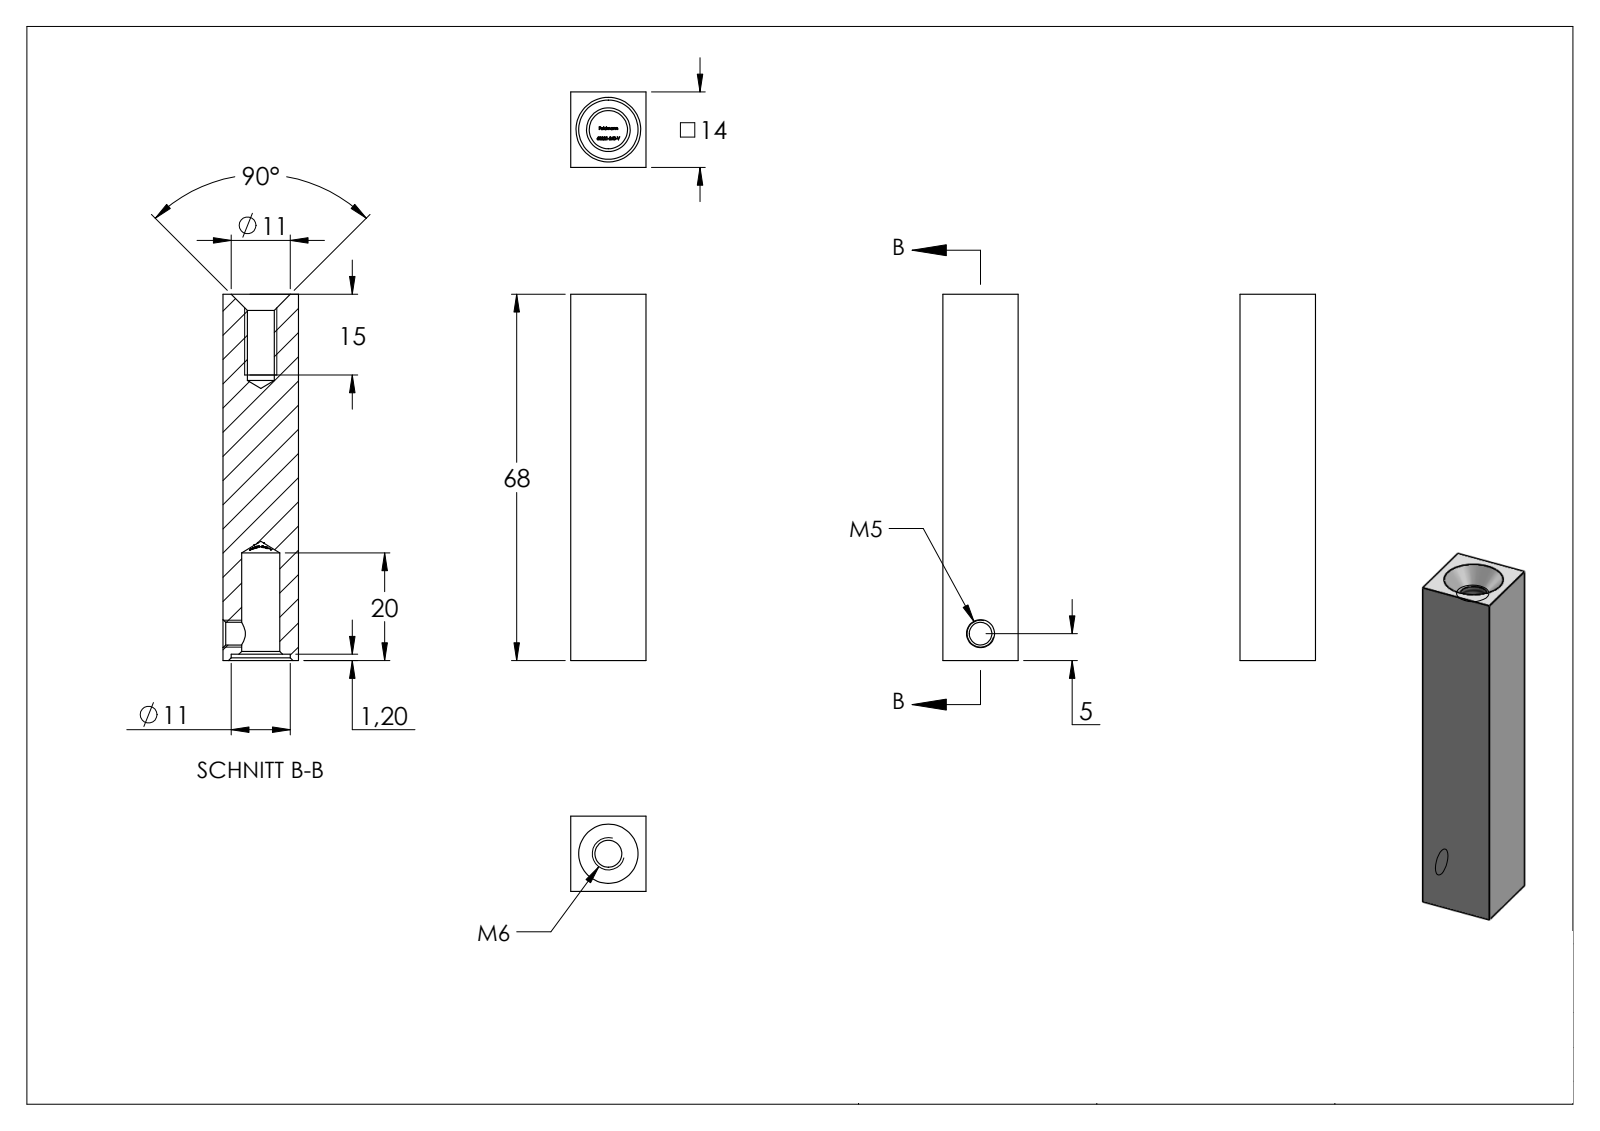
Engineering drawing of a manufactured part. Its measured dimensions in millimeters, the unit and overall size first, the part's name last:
Units: millimetres
Overall size (bounding box): 82.8 × 70 × 14
Round holes (diameter × count): ⌀4.2 ×1, ⌀5 ×1, ⌀7.1 ×1, ⌀11 ×1
Round bosses / shafts (diameter × count): ⌀10.5 ×1, ⌀8 ×1, ⌀7 ×1, ⌀6 ×1, ⌀5 ×1
Main face-to-face distances: 14, 66.8, 1.2, 68, 1, 67.8, 15, 16, 14.8, 82.8
Volume: 13 314 mm³ · Surface area: 5 910 mm²
Bodies: 3 solids, 297 faces (135 planar, 10 cylindrical, 152 other)
Part name (STEP PRODUCT): DIN914_DIN 914 M5x4; 60221-240-V Teil2_60221-240-V Teil2; 60221-240-V; DIN914 (+3 more)
STEP written by: SolidWorks 2015 (CONFIG_CONTROL_DESIGN)
